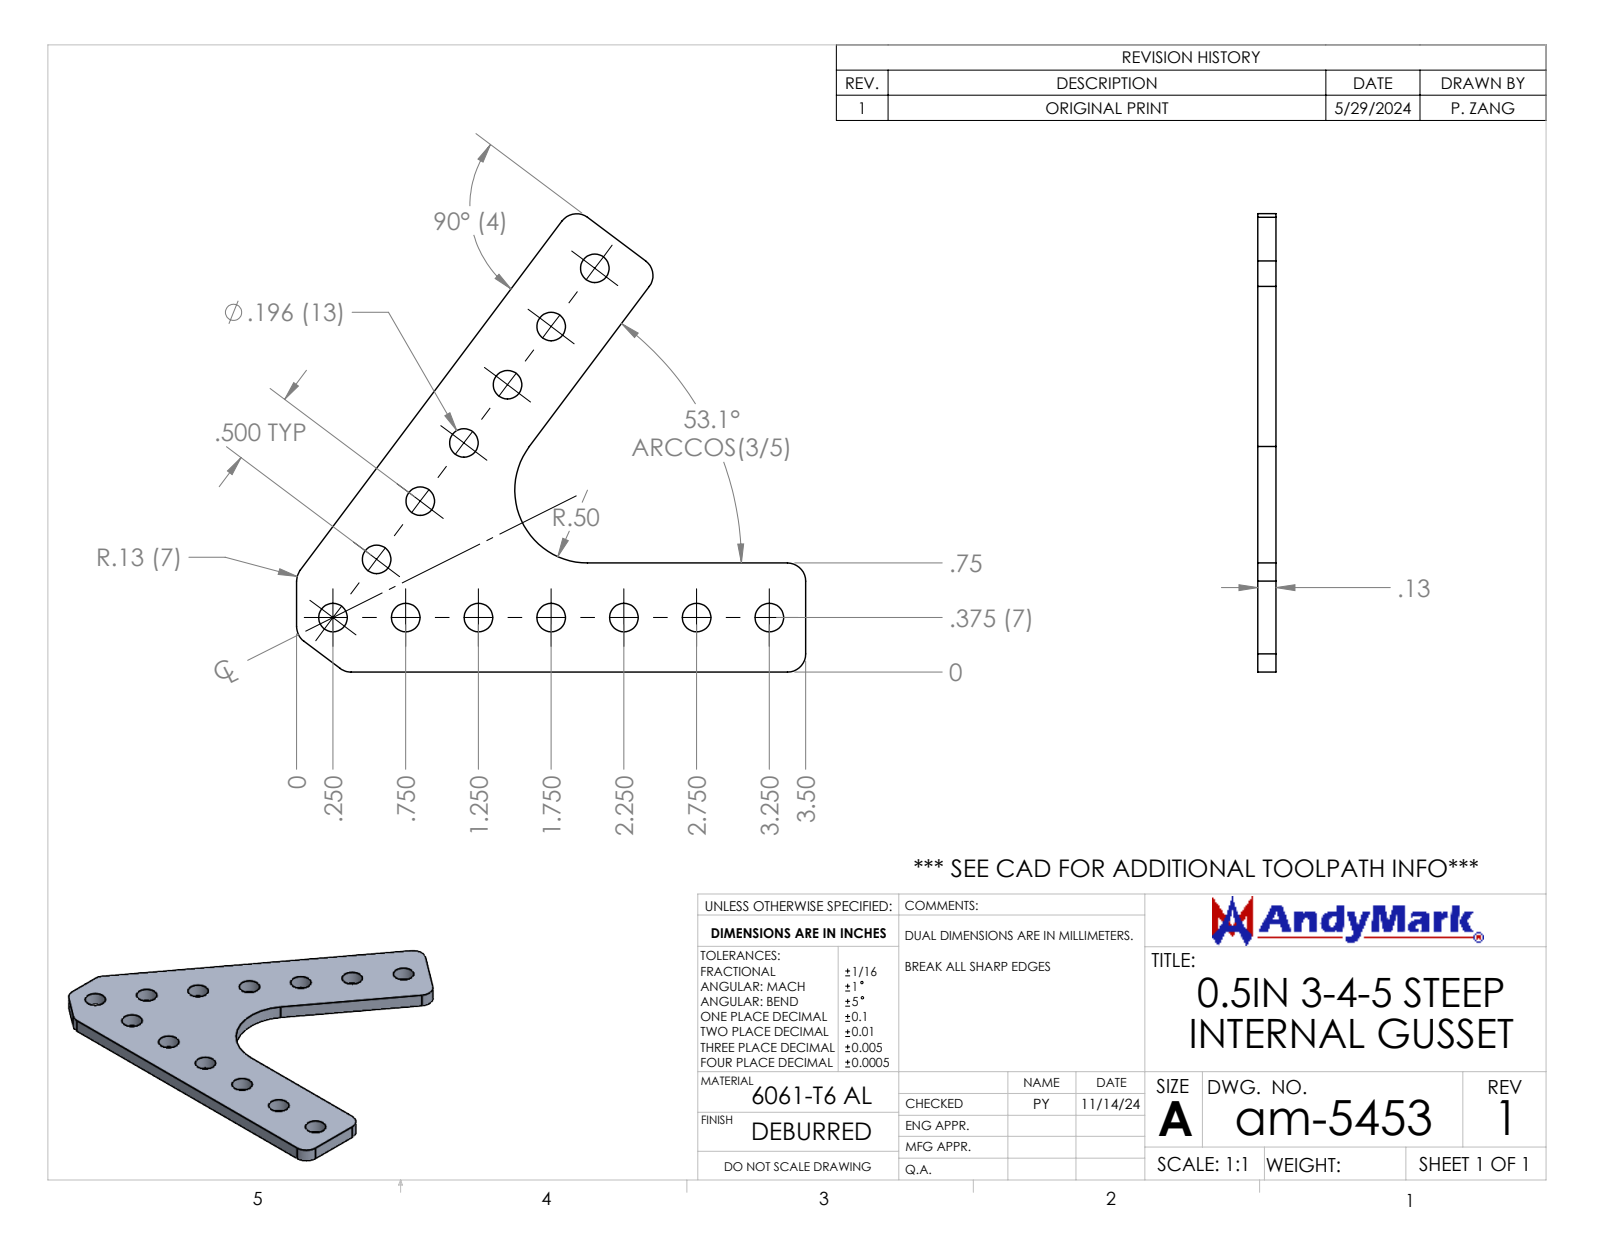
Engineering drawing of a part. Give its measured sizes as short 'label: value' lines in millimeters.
name: am-5453 0.5IN 3-4-5 Steep Internal Gusset
written by: SolidWorks 2024 (CONFIG_CONTROL_DESIGN)
unit: mm
bodies: 1 solid, 45 faces (10 planar, 35 cylindrical, 0 other)
size: 88.9 × 80 × 3.2
volume: 9 180 mm³; area: 7 445 mm²
holes: 13× ⌀5
rounds: 7× R3.2, 1× R12.7
face distances: 3.2, 19.1, 88.9
hole spacings: 12.7, 25.4, 38.1, 50.8, 63.5, 52.3, 56.8, 20.5
